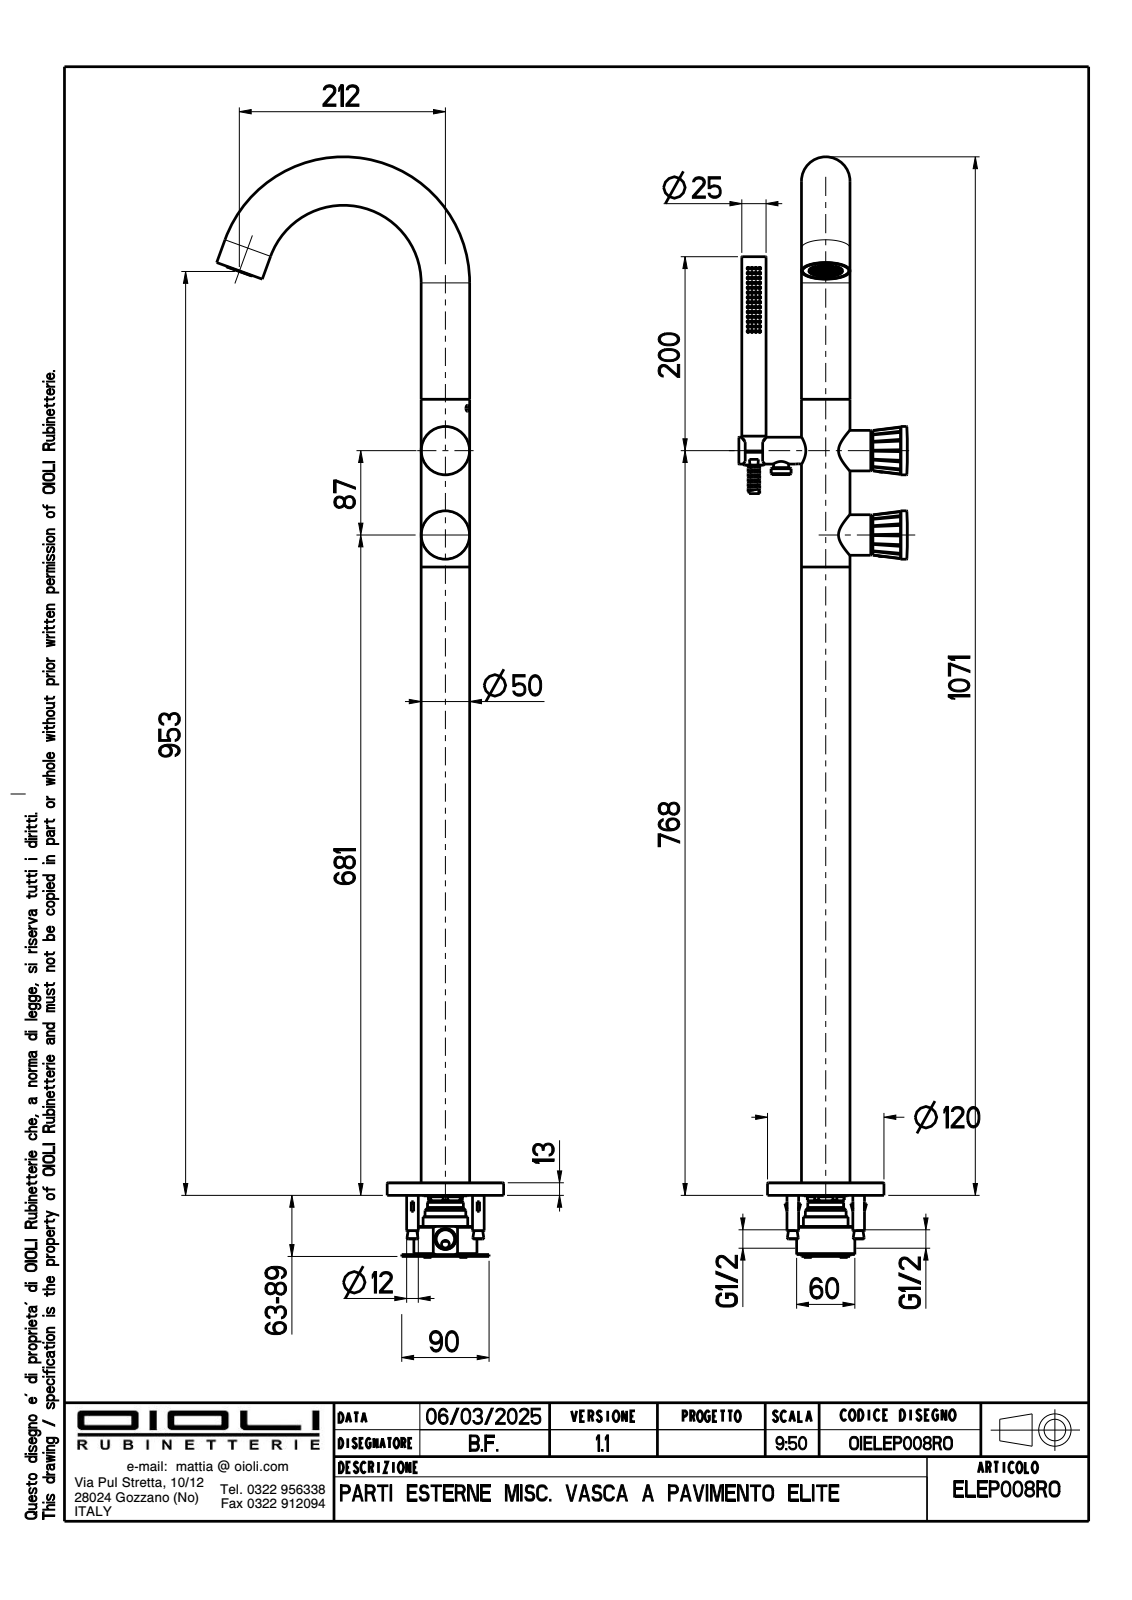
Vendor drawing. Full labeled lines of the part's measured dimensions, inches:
Part name (STEP PRODUCT): OICT00012; OIBR00163; OIBR00258; OIBR00254 (+8 more)
STEP written by: CREO PARAMETRIC BY PTC INC, 2024493 (CONFIG_CONTROL_DESIGN)
Units: inches
Bodies: 25 solids, 6440 faces (4362 planar, 828 cylindrical, 1250 other)
Overall size (bounding box): 42.165 × 11.642 × 6.839
Volume: 51.56 in³ · Surface area: 829.1 in²
Round holes (diameter × count): ⌀0.197 ×6, ⌀0.315 ×6, ⌀0.354 ×4, ⌀0.433 ×4, ⌀0.256 ×3, ⌀1.201 ×3, ⌀0.165 ×2, ⌀0.244 ×2, ⌀0.374 ×2, ⌀0.591 ×2, ⌀0.65 ×2, ⌀0.768 ×2
Round bosses / shafts (diameter × count): ⌀0.394 ×4, ⌀0.236 ×4, ⌀1.496 ×3, ⌀1.969 ×2, ⌀1.965 ×2, ⌀1.811 ×2, ⌀1.646 ×2, ⌀1.575 ×2
Partial cylindrical surfaces — rounded edges, fillets, slot ends (radius × count): R0.005 ×89, R0.004 ×20, R0.008 ×16, R0.197 ×4, R0.268 ×4, R0.394 ×2, R0.151 ×1, R0.157 ×1
Main face-to-face distances: 0.079, 3.035, 31.89, 31.811, 24.803, 24.724, 7.087, 0.512, 0.433, 0.945
Hole centre spacings: 0.406, 0.53, 2.857, 3.052, 0.197, 0.339, 0.363, 0.481
